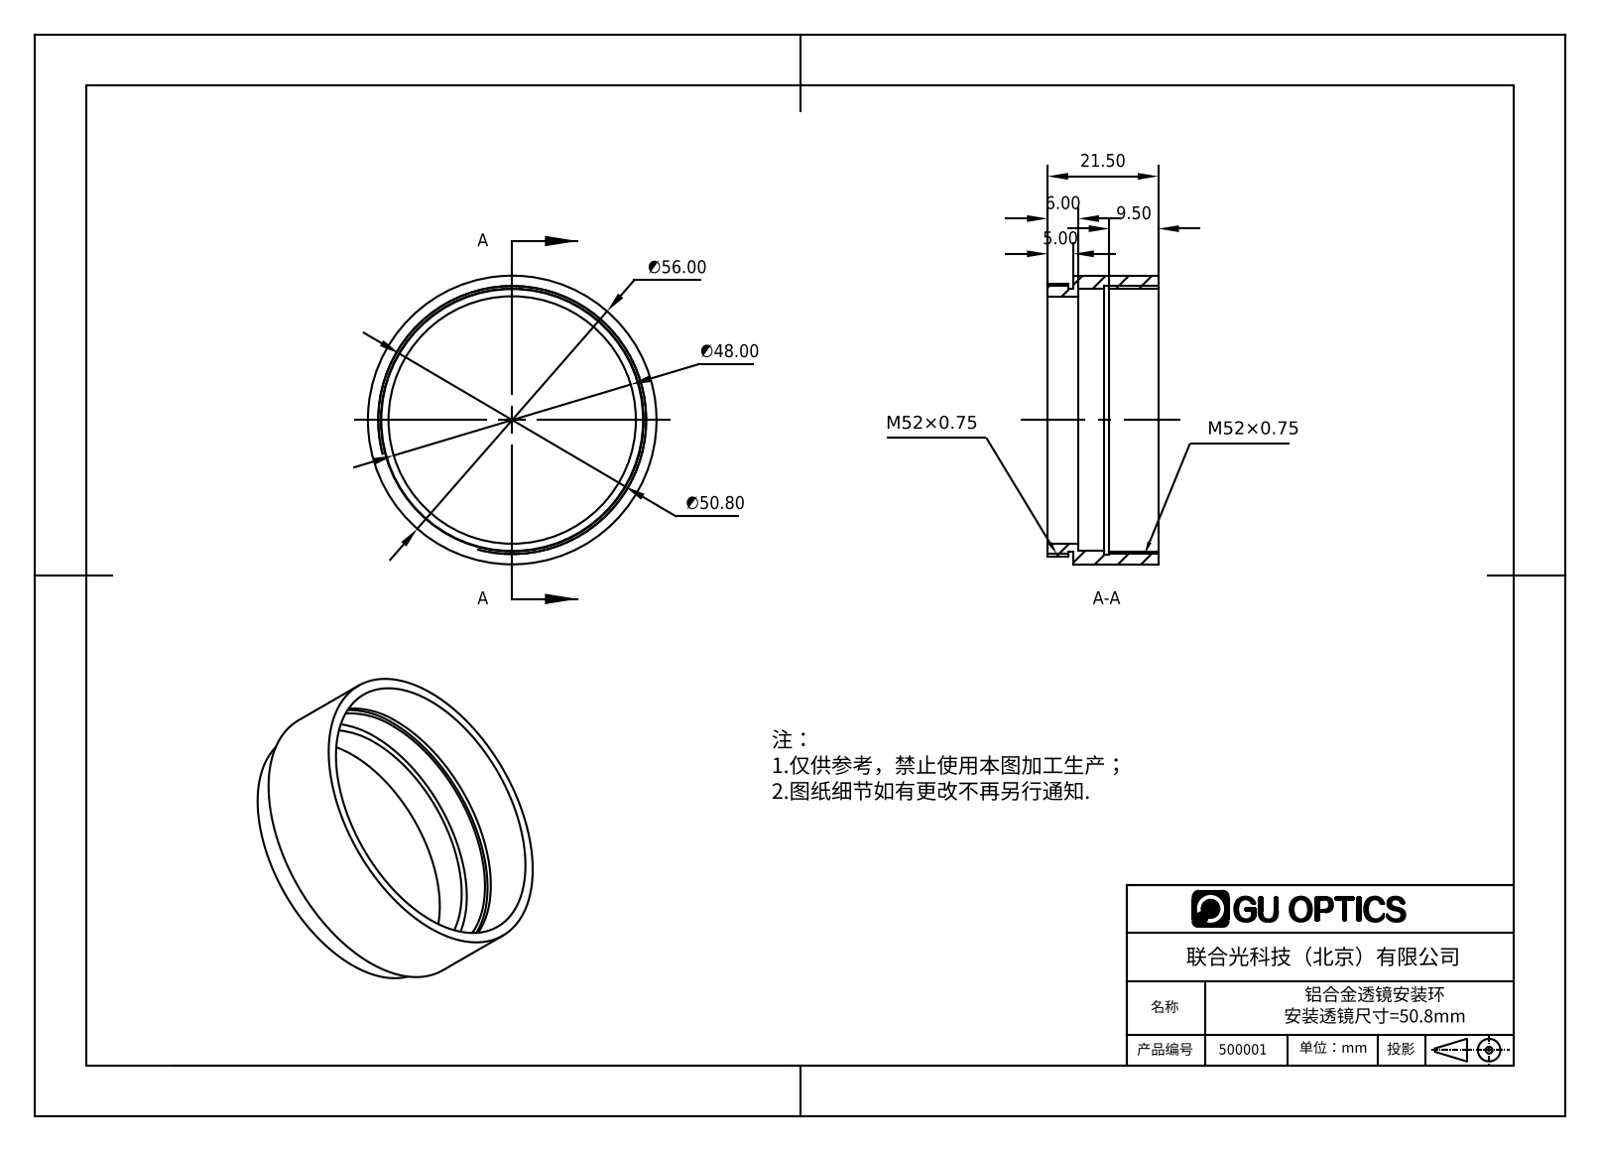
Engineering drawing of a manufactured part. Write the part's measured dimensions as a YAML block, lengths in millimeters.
part_name: "500001"
step_written_by: "SolidWorks 2016 (AUTOMOTIVE_DESIGN)"
units: millimeters
bodies: {solids: 1, faces: 21, planar: 7, cylindrical: 14, other: 0}
overall_size: [56, 56, 21.5]
volume: 8969
surface_area: 8946
round_holes:
  - {diameter: 48, count: 1}
  - {diameter: 50.8, count: 1}
  - {diameter: 51, count: 1}
  - {diameter: 52.2, count: 1}
round_bosses_or_shafts:
  - {diameter: 56, count: 1}
  - {diameter: 53, count: 1}
face_to_face_distances: [5, 1, 6, 16.5, 21.5, 15.5, 7, 4, 2, 17.5]
